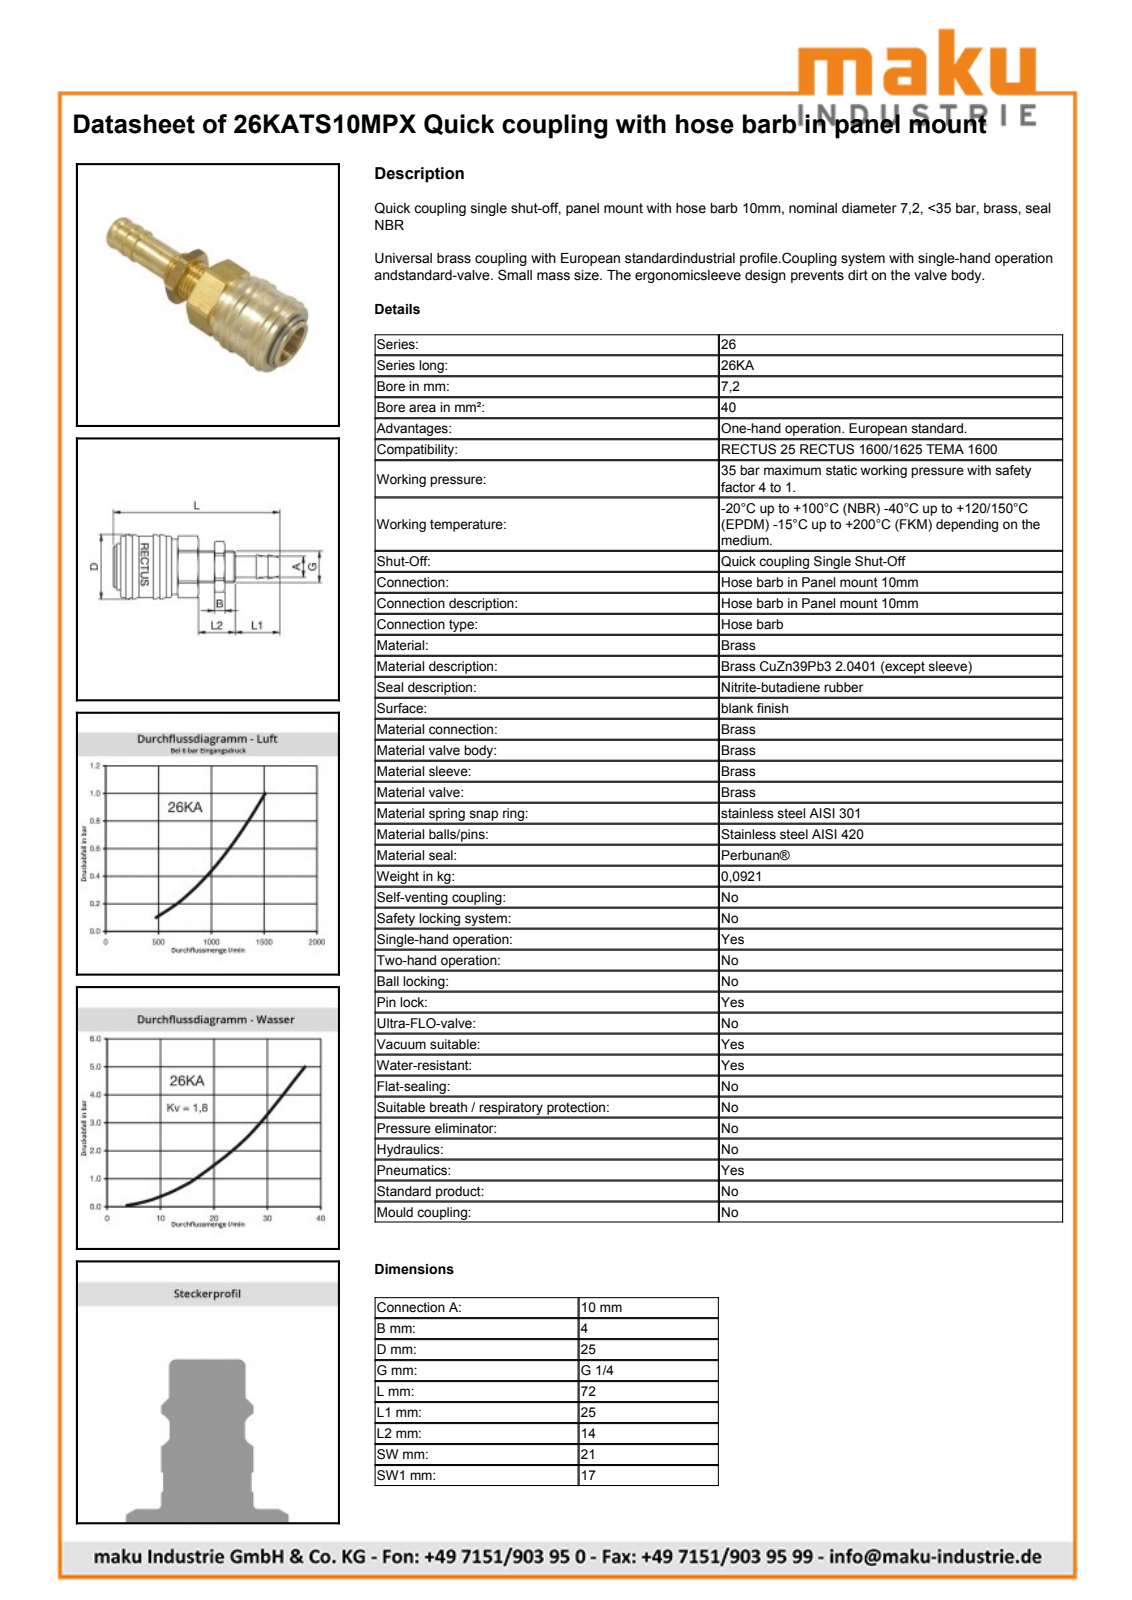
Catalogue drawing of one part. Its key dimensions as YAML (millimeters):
part_name: "D113525"
step_written_by: "Autodesk Inventor 2013 (AUTOMOTIVE_DESIGN)"
units: millimeters
bodies: {solids: 2, faces: 496, planar: 183, cylindrical: 69, other: 244}
overall_size: [72, 24.8, 24.8]
volume: 15618
surface_area: 8529
round_holes:
  - {diameter: 15.45, count: 1}
  - {diameter: 16.1, count: 1}
  - {diameter: 17, count: 1}
  - {diameter: 21.1, count: 1}
round_bosses_or_shafts:
  - {diameter: 23.3, count: 1}
  - {diameter: 21, count: 1}
  - {diameter: 18, count: 1}
  - {diameter: 16.65, count: 1}
  - {diameter: 15.95, count: 1}
  - {diameter: 15.15, count: 1}
  - {diameter: 14.95, count: 1}
  - {diameter: 13.16, count: 1}
partial_cylinders:
  - {radius: 9.57, count: 1}
  - {radius: 11.55, count: 1}
  - {radius: 11.85, count: 1}
face_to_face_distances: [21, 30.35, 2.65, 33, 3.5, 18.35, 12, 17, 72, 69.35]
